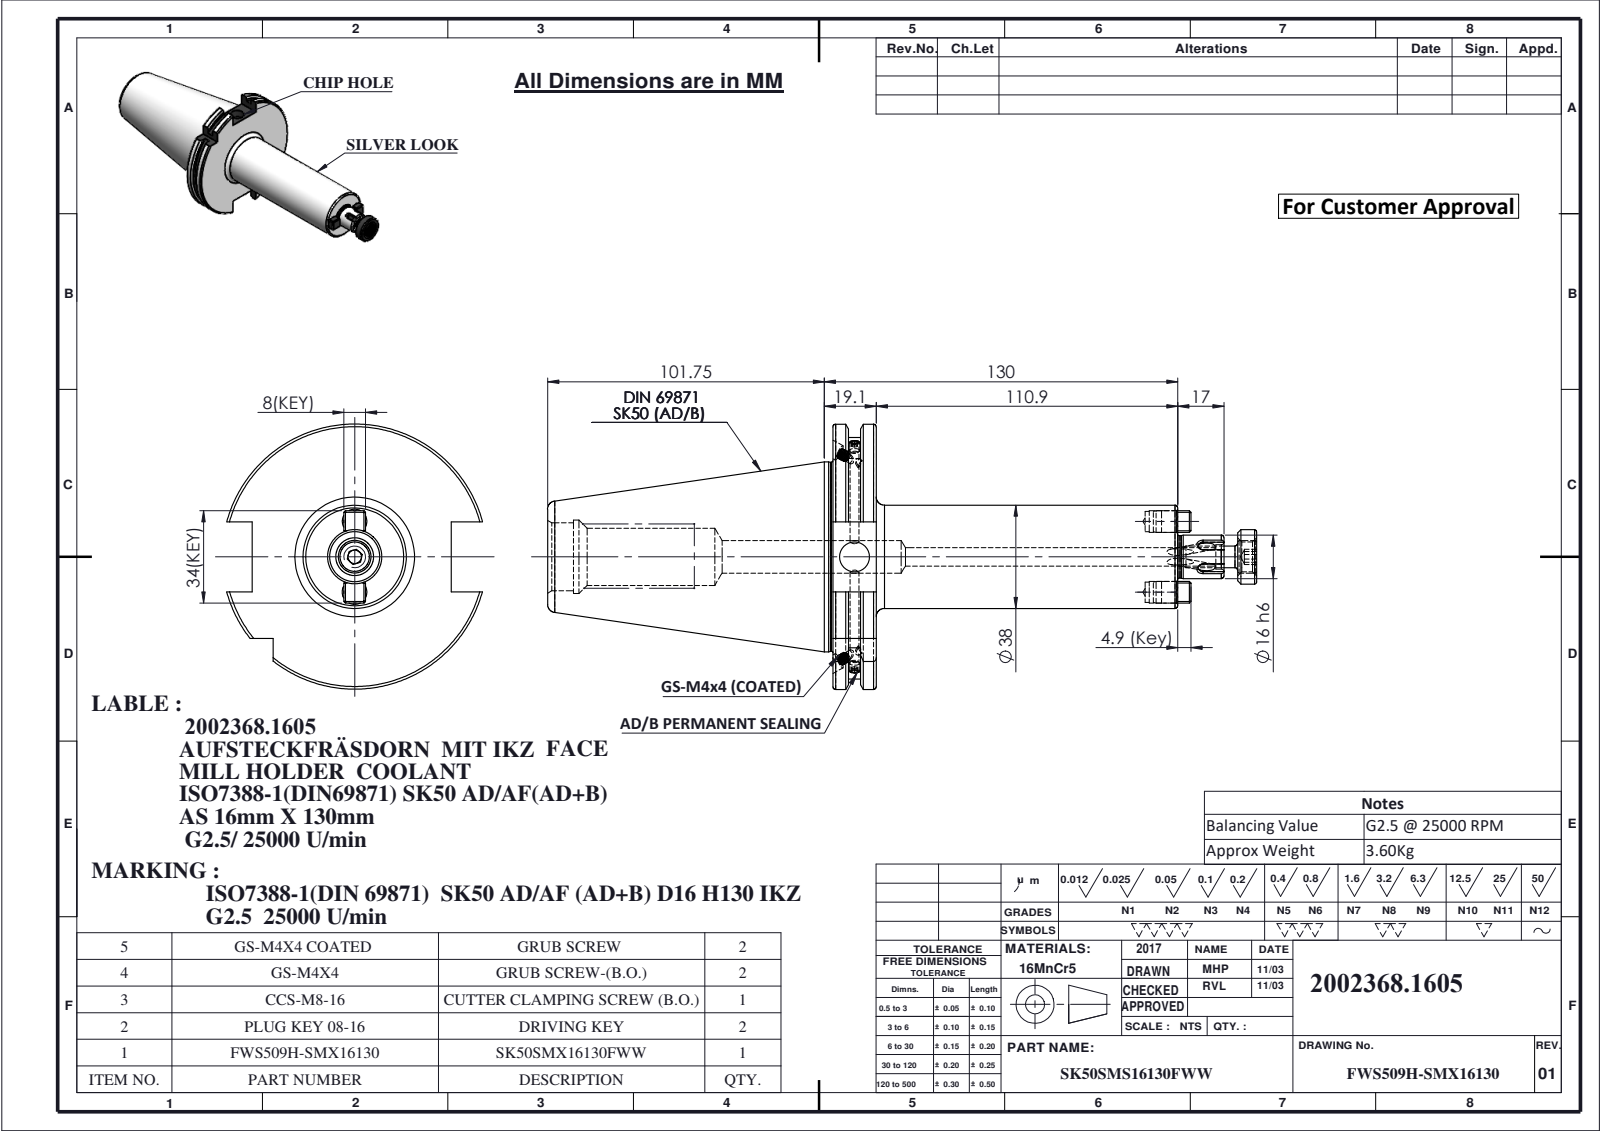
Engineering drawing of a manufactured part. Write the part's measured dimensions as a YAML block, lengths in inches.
part_name: "CCS-M8-16-1; FWS509H-SMX16130; SK50SMX16130FWW; M4X4_DIN 913 - M4 x 4-N (+4 more)"
step_written_by: "SolidWorks 2024 (CONFIG_CONTROL_DESIGN)"
units: inches
bodies: {solids: 9, faces: 440, planar: 130, cylindrical: 127, other: 183}
overall_size: [10.266, 3.839, 3.703]
volume: 27.97
surface_area: 100.3
round_holes:
  - {diameter: 0.118, count: 4}
  - {diameter: 0.126, count: 2}
  - {diameter: 0.236, count: 2}
  - {diameter: 0.295, count: 2}
  - {diameter: 0.315, count: 2}
  - {diameter: 0.433, count: 2}
  - {diameter: 0.13, count: 1}
  - {diameter: 0.268, count: 1}
  - {diameter: 0.354, count: 1}
  - {diameter: 0.472, count: 1}
  - {diameter: 0.827, count: 1}
  - {diameter: 0.984, count: 1}
round_bosses_or_shafts:
  - {diameter: 0.157, count: 4}
  - {diameter: 0.316, count: 2}
  - {diameter: 0.314, count: 2}
  - {diameter: 0.114, count: 2}
  - {diameter: 2.75, count: 1}
  - {diameter: 2.734, count: 1}
  - {diameter: 1.496, count: 1}
  - {diameter: 0.787, count: 1}
partial_cylinders:
  - {radius: 0.079, count: 4}
  - {radius: 0.207, count: 2}
  - {radius: 1.768, count: 1}
  - {radius: 1.919, count: 1}
face_to_face_distances: [0.626, 4.992, 4.366, 0.223, 0.403, 4.769, 0.4, 0.177, 0.226, 4.593]
hole_center_spacings: [0.512, 1.024]
